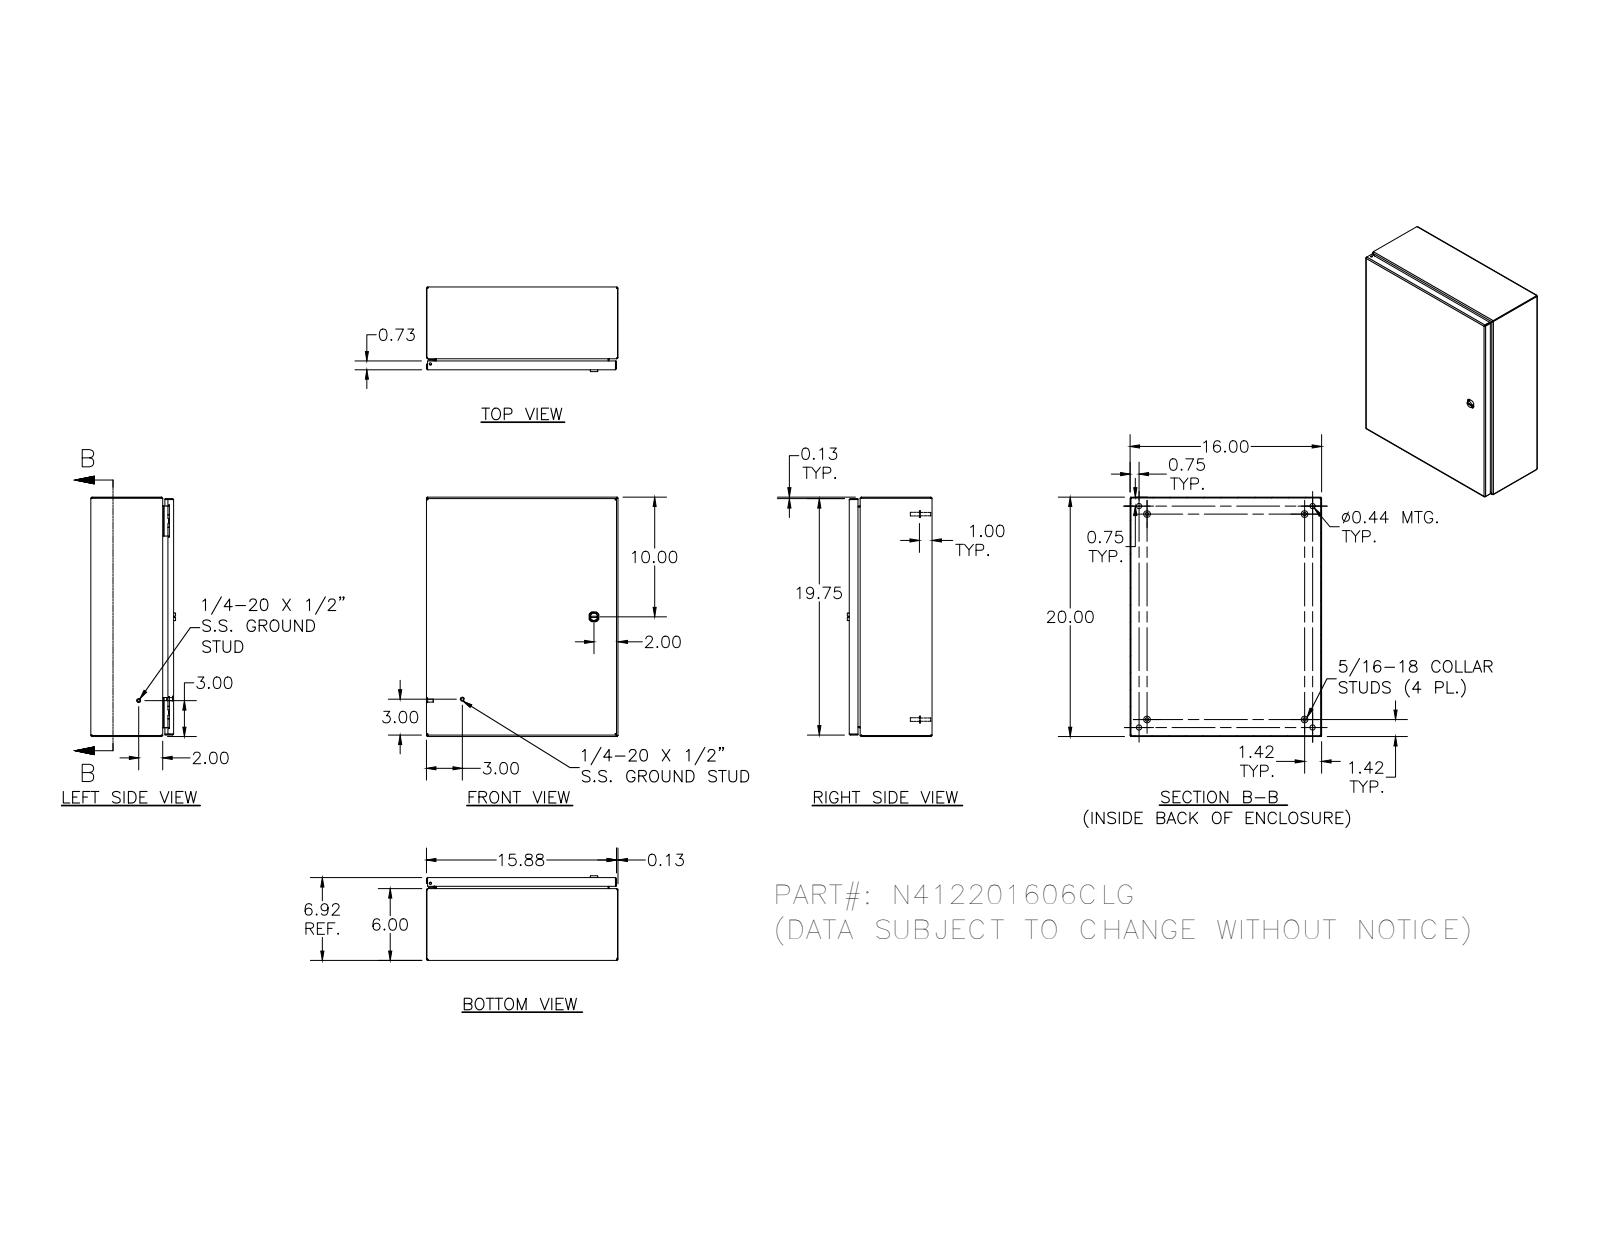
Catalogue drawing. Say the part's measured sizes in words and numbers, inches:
The part is named "N412201606CLG". Its 3-D file was written by "SolidWorks 2018 (AUTOMOTIVE_DESIGN)". It is 33 solids with 1449 faces: 530 planar, 547 cylindrical and 372 other. Overall it measures 20 by 16 by 7.075 inches. Its volume is 90.39 cubic inches and its surface area 2 460 square inches. Round holes: 5 of diameter 0.188, 4 of diameter 0.093, 4 of diameter 0.152, 4 of diameter 0.167, 4 of diameter 0.172, 4 of diameter 0.437, 2 of diameter 0.156, 1 of diameter 0.187, 1 of diameter 0.197, 1 of diameter 0.315, 1 of diameter 0.394, 1 of diameter 0.402. Round bosses or shafts: 10 of diameter 0.25, 5 of diameter 0.131, 4 of diameter 0.563, 4 of diameter 0.36, 4 of diameter 0.32, 4 of diameter 0.3, 4 of diameter 0.275, 4 of diameter 0.256. Partial cylindrical surfaces (rounded edges, fillets, slot ends): 30 of radius 0.012, 30 of radius 0.031, 26 of radius 0.05, 20 of radius 0.105, 18 of radius 0.016, 16 of radius 0.125, 13 of radius 0.02, 8 of radius 0.032. The main face-to-face distances are 0.074, 6.843, 6.769, 6.917, 0.074, 15.926, 16, 15.852, 15.926, 20. The hole center spacings are 16, 0.66, 0.656, 1.307, 1.965, 15.34, 16.66, 15.614.
